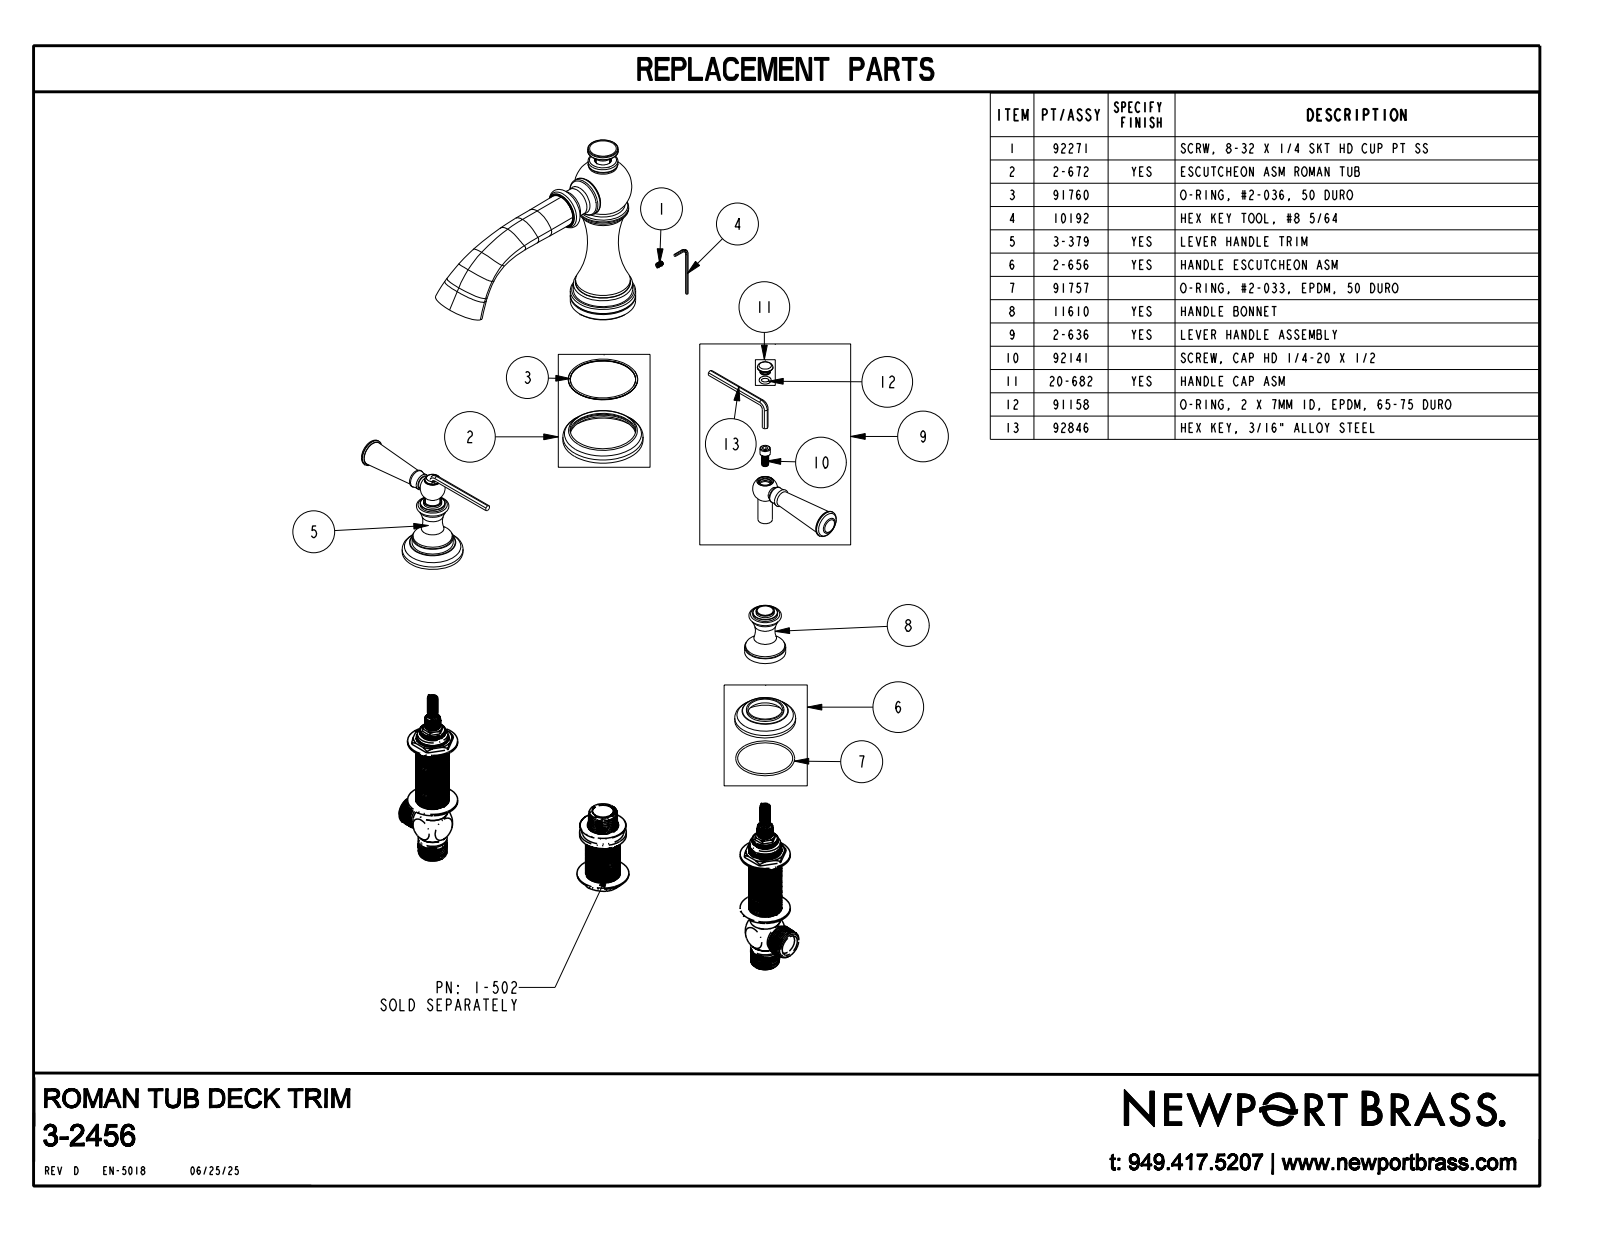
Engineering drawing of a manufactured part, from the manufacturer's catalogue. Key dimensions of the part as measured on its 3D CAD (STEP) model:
Part name (STEP PRODUCT): 3-2456
STEP written by: CREO PARAMETRIC BY PTC INC, 2018400 (CONFIG_CONTROL_DESIGN)
Units: inches
Bodies: 3 solids, 271 faces (33 planar, 56 cylindrical, 182 other)
Overall size (bounding box): 14.6 × 9.298 × 6.92
Volume: 32.26 in³ · Surface area: 126.1 in²
Round bosses / shafts (diameter × count): ⌀2.2 ×2, ⌀1.49 ×2, ⌀1.42 ×2, ⌀0.9 ×2, ⌀0.66 ×2, ⌀0.56 ×2, ⌀0.517 ×2, ⌀2.9 ×1
Main face-to-face distances: 0.43, 0.08, 6.29, 5.86, 2.17, 1.74, 4.12, 4.2, 2.09, 1.66
